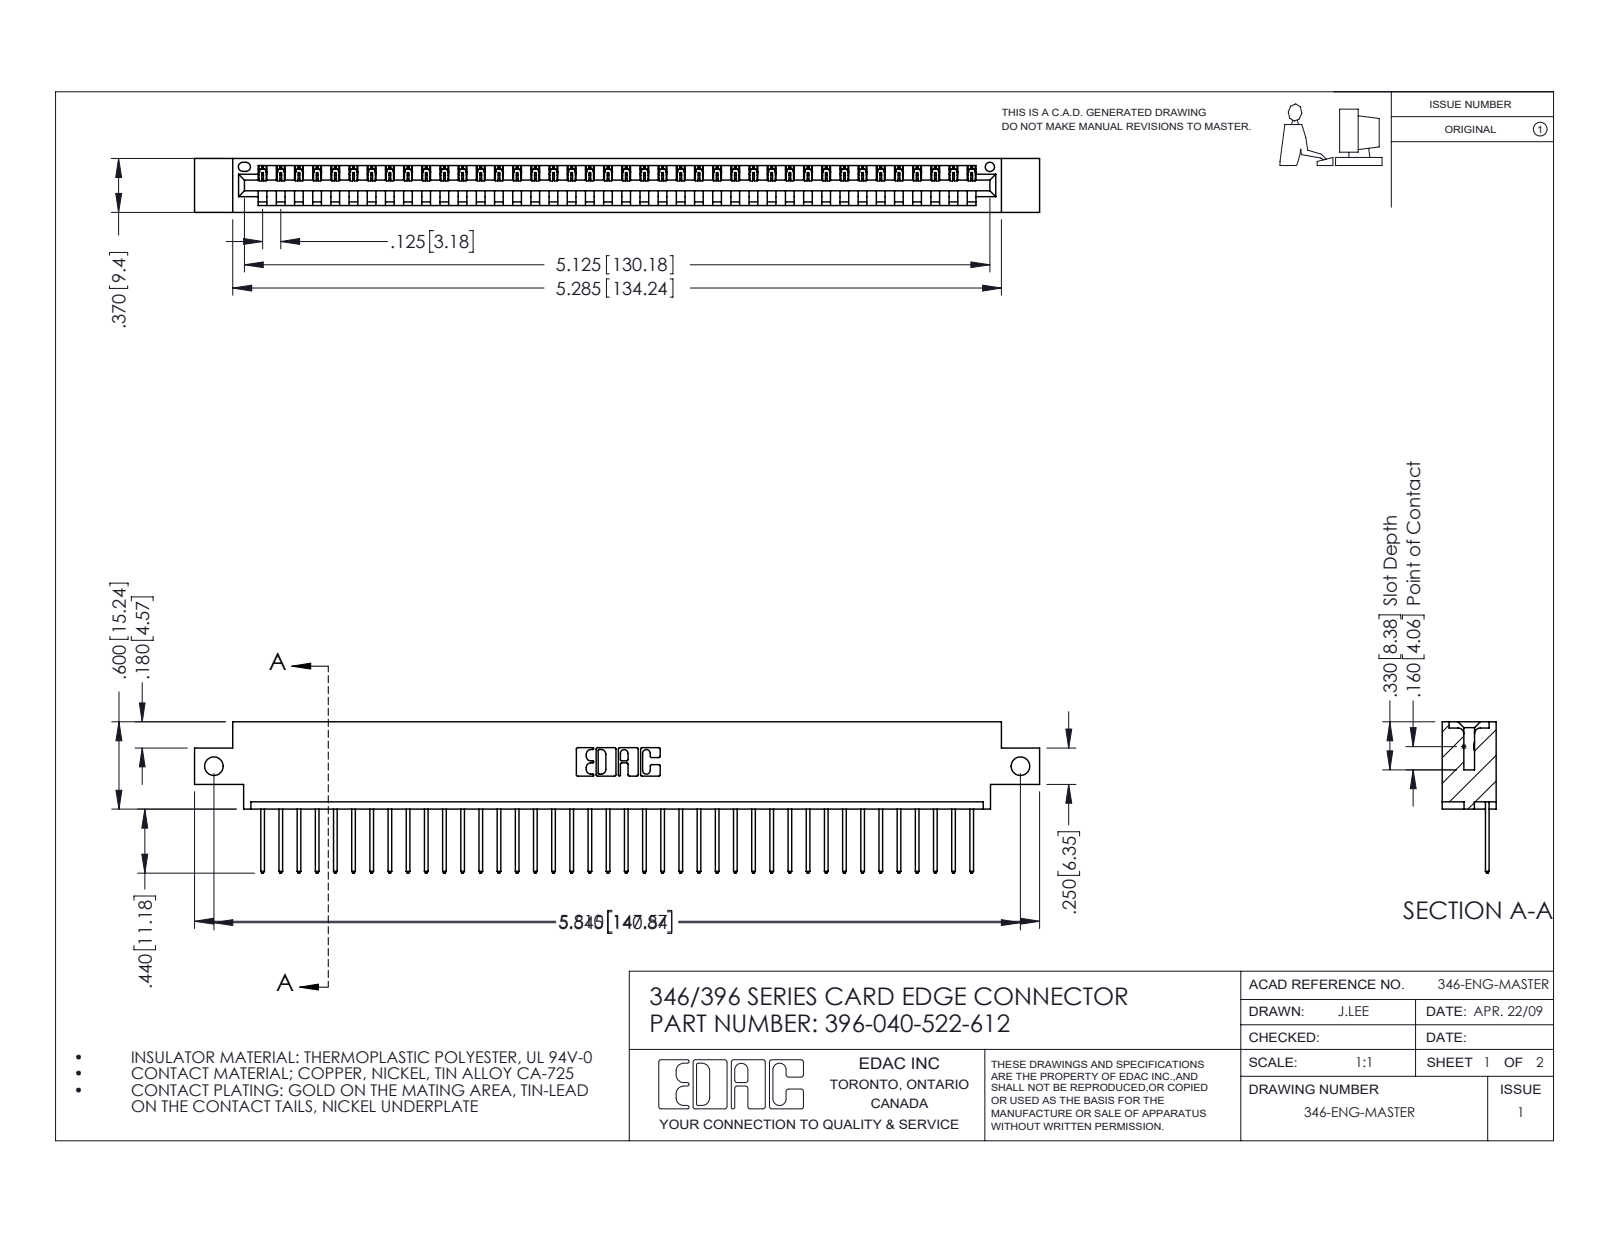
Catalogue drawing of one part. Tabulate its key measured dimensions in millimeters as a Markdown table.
| quantity | value |
| --- | --- |
| part name | 345-292-001_345-293-122; 396-040-522-612; 346 Part_0.170 Offset - Side Mount |
| STEP written by | SolidWorks 2016 (CONFIG_CONTROL_DESIGN) |
| units | millimeters |
| bodies | 41 solids, 2446 faces (1680 planar, 766 cylindrical, 0 other) |
| overall size | 147.6 × 26.4 × 9.4 |
| volume | 13 900 mm³ |
| surface area | 17 480 mm² |
| round holes (diameter × count) | 3.3 × 2, 1.6 × 1 |
| partial cylindrical surfaces (radius × count) | 0.2 × 80, 0.3 × 80, 0.3 × 22, 0.2 × 6, 0.8 × 6, 0.7 × 3, 0.8 × 2, 1 × 2 |
| main face-to-face distances | 1.2, 8.2, 9.4, 6.4, 1.8, 7.6, 0.6, 3.8, 5.6, 2.5 |
| hole center spacings | 140.8 |
